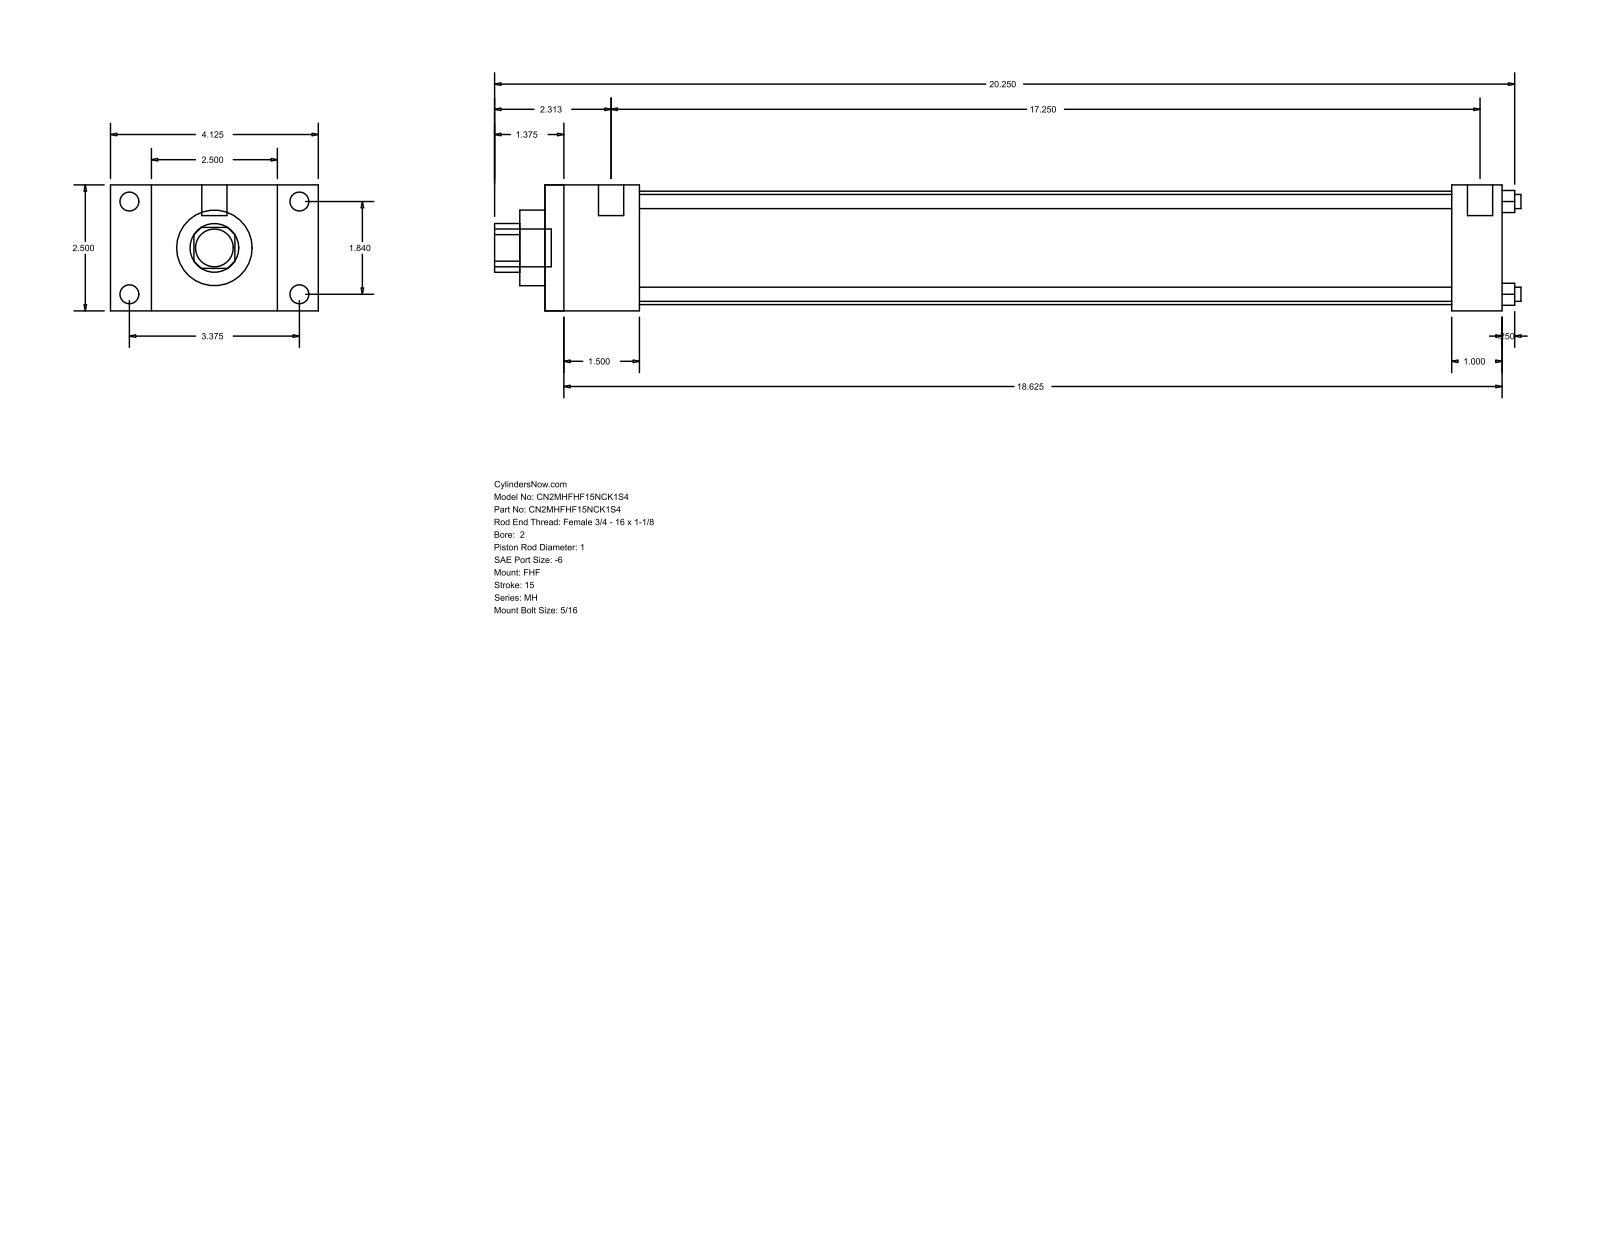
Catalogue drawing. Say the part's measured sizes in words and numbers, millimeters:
The part is named "MH_FHF__0200_1". Its 3-D file was written by "GSSL Pune (CONFIG_CONTROL_DESIGN)". It is 0 solids with 88 faces: 60 planar, 28 cylindrical and 0 other. Overall it measures 517.52 by 104.78 by 63.5 millimeters. Round holes: 4 of diameter 7.14, 1 of diameter 25.4, 1 of diameter 38.1, 1 of diameter 57.15. Round bosses or shafts: 4 of diameter 9.53, 4 of diameter 5.56, 2 of diameter 12.7, 1 of diameter 19.05. Partial cylindrical surfaces (rounded edges, fillets, slot ends): 1 of radius 12.29. The main face-to-face distances are 63.5, 482.6, 47.63, 434.97, 20.64, 84.14, 104.78, 25.4, 457.2, 409.57. The hole center spacings are 33.05, 46.74, 66.1.
